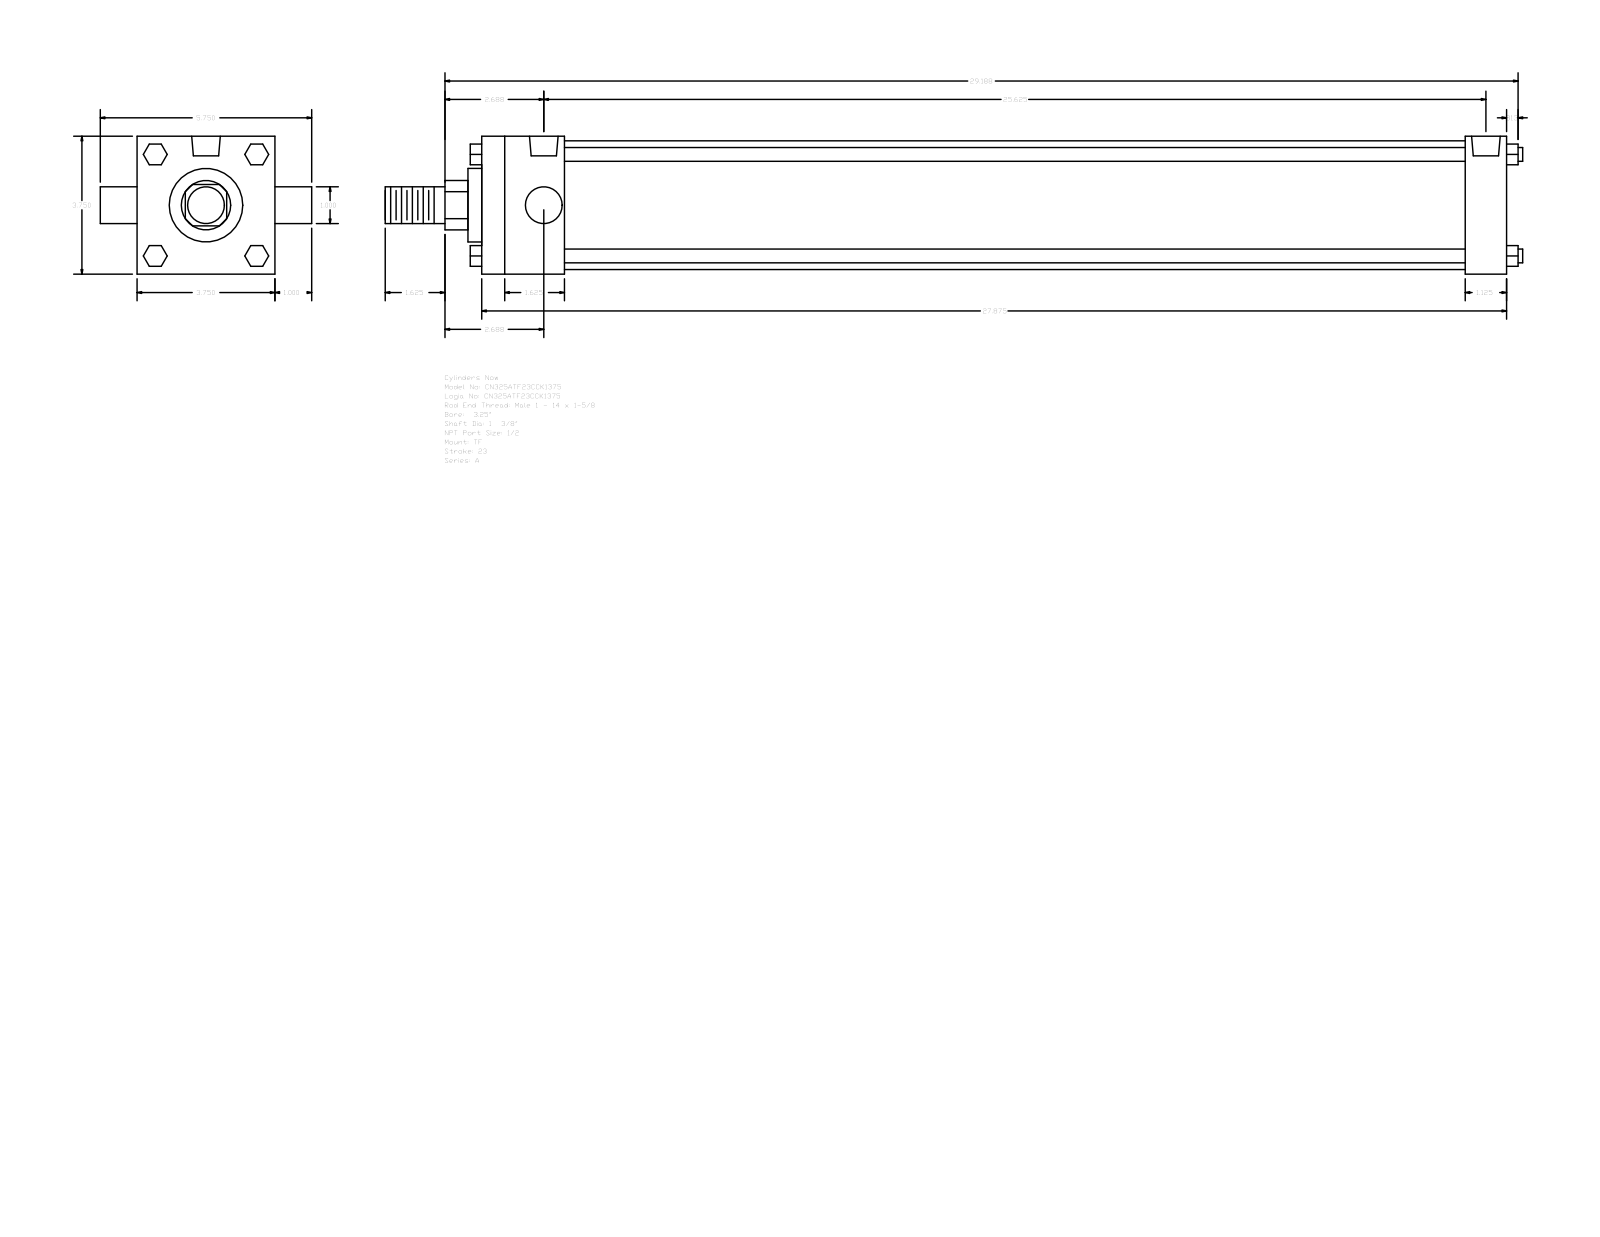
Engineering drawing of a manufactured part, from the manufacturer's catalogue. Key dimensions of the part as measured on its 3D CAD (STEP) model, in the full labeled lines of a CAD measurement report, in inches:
Part name (STEP PRODUCT): A_TF__0325_1.375
STEP written by: GSSL Pune (CONFIG_CONTROL_DESIGN)
Units: inches
Bodies: 0 solids, 120 faces (92 planar, 28 cylindrical, 0 other)
Overall size (bounding box): 30.937 × 5.75 × 3.75
Round holes (diameter × count): ⌀0.344 ×3, ⌀0.778 ×2
Round bosses / shafts (diameter × count): ⌀0.375 ×4, ⌀1 ×2, ⌀3.5 ×1, ⌀2 ×1, ⌀1.375 ×1
Partial cylindrical surfaces — rounded edges, fillets, slot ends (radius × count): R0.672 ×1
Main face-to-face distances: 3.75, 27.875, 2.25, 26.75, 24.5, 25.625, 1.125, 2.625, 0.375, 27.125
Hole centre spacings: 0.125, 25.5, 25.375, 25.625
